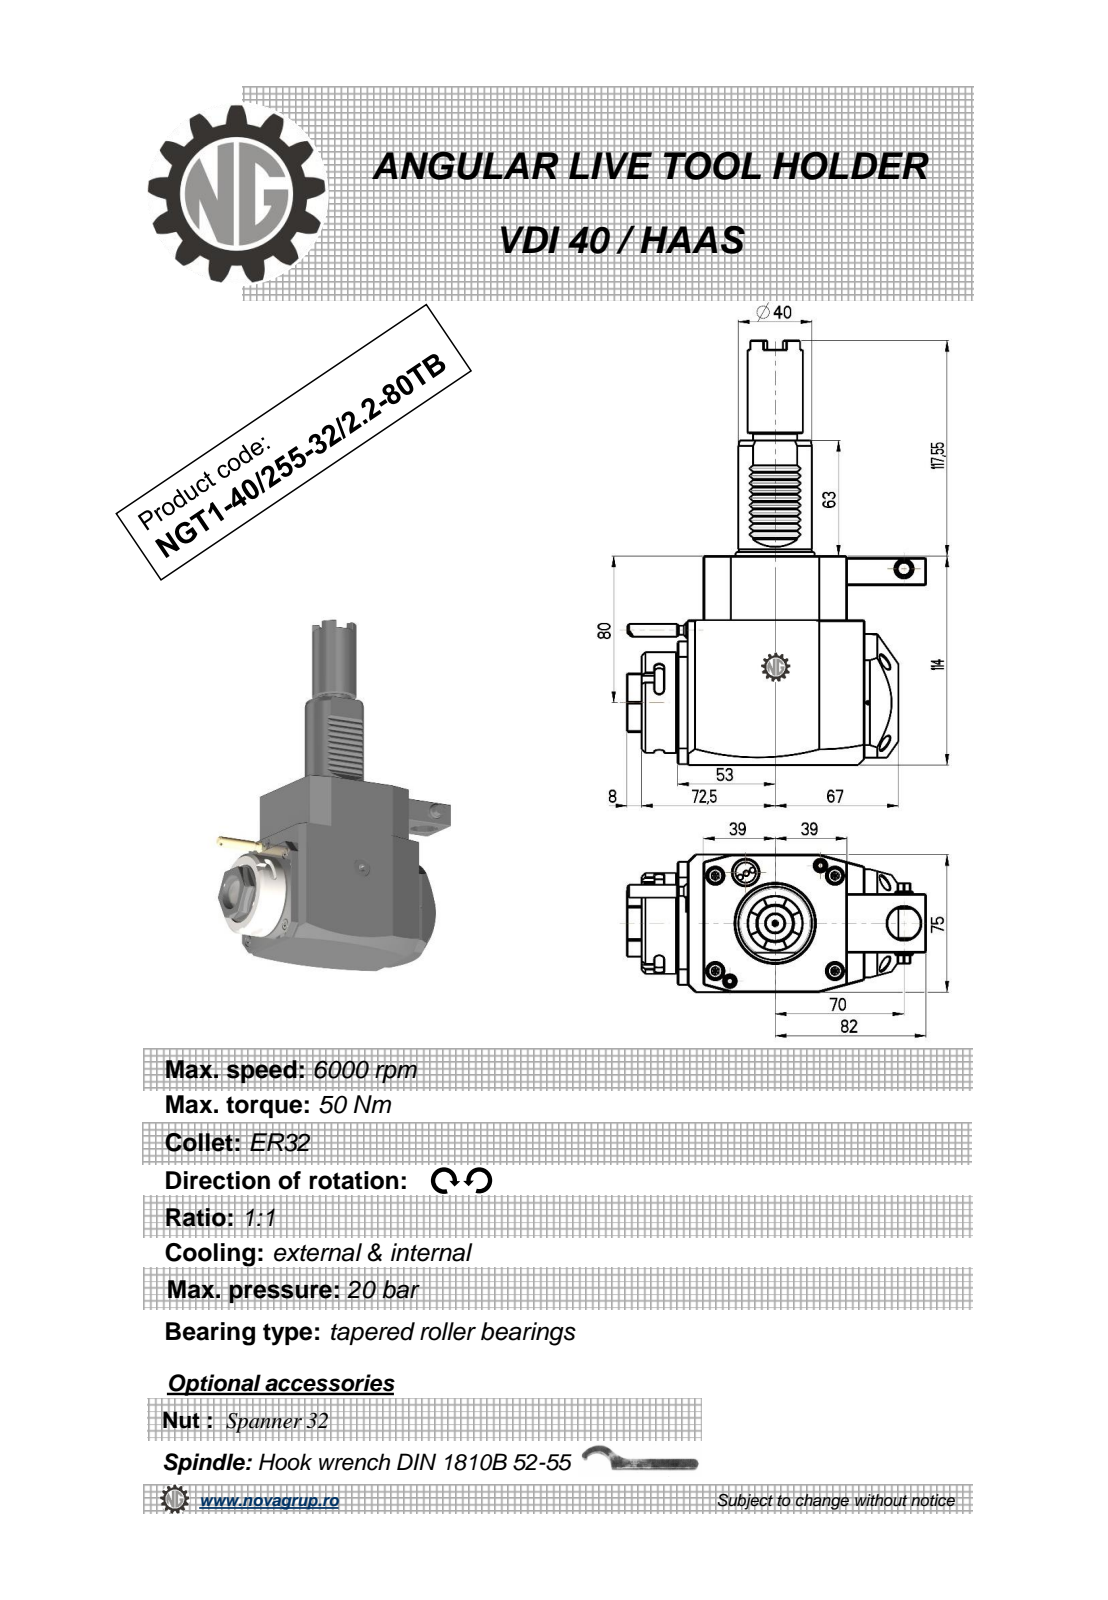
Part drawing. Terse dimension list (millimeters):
name: NGT1_40_255_32_1_2_80TB
written by: PRO/ENGINEER BY PARAMETRIC TECHNOLOGY CORPORATION, 2010280 (CONFIG_CONTROL_DESIGN)
unit: mm
bodies: 1 solid, 385 faces (219 planar, 82 cylindrical, 84 other)
size: 231.55 × 162.5 × 75
volume: 1 004 000 mm³; area: 78 738 mm²
holes: 1× ⌀2.5, 1× ⌀3, 1× ⌀9.5, 1× ⌀18, 1× ⌀20, 1× ⌀23
bosses: 2× ⌀8.96, 1× ⌀55, 1× ⌀48, 1× ⌀40, 1× ⌀30, 1× ⌀24, 1× ⌀10, 1× ⌀7
rounds: 10× R0.3, 6× R2.5, 2× R180, 1× R0.5, 1× R3.85, 1× R4.25, 1× R24.5, 1× R37.5
face distances: 75, 114, 14, 33.5, 79, 92, 78, 21.5, 98, 19.5
hole spacings: 37.35, 43.2, 70, 72.5
